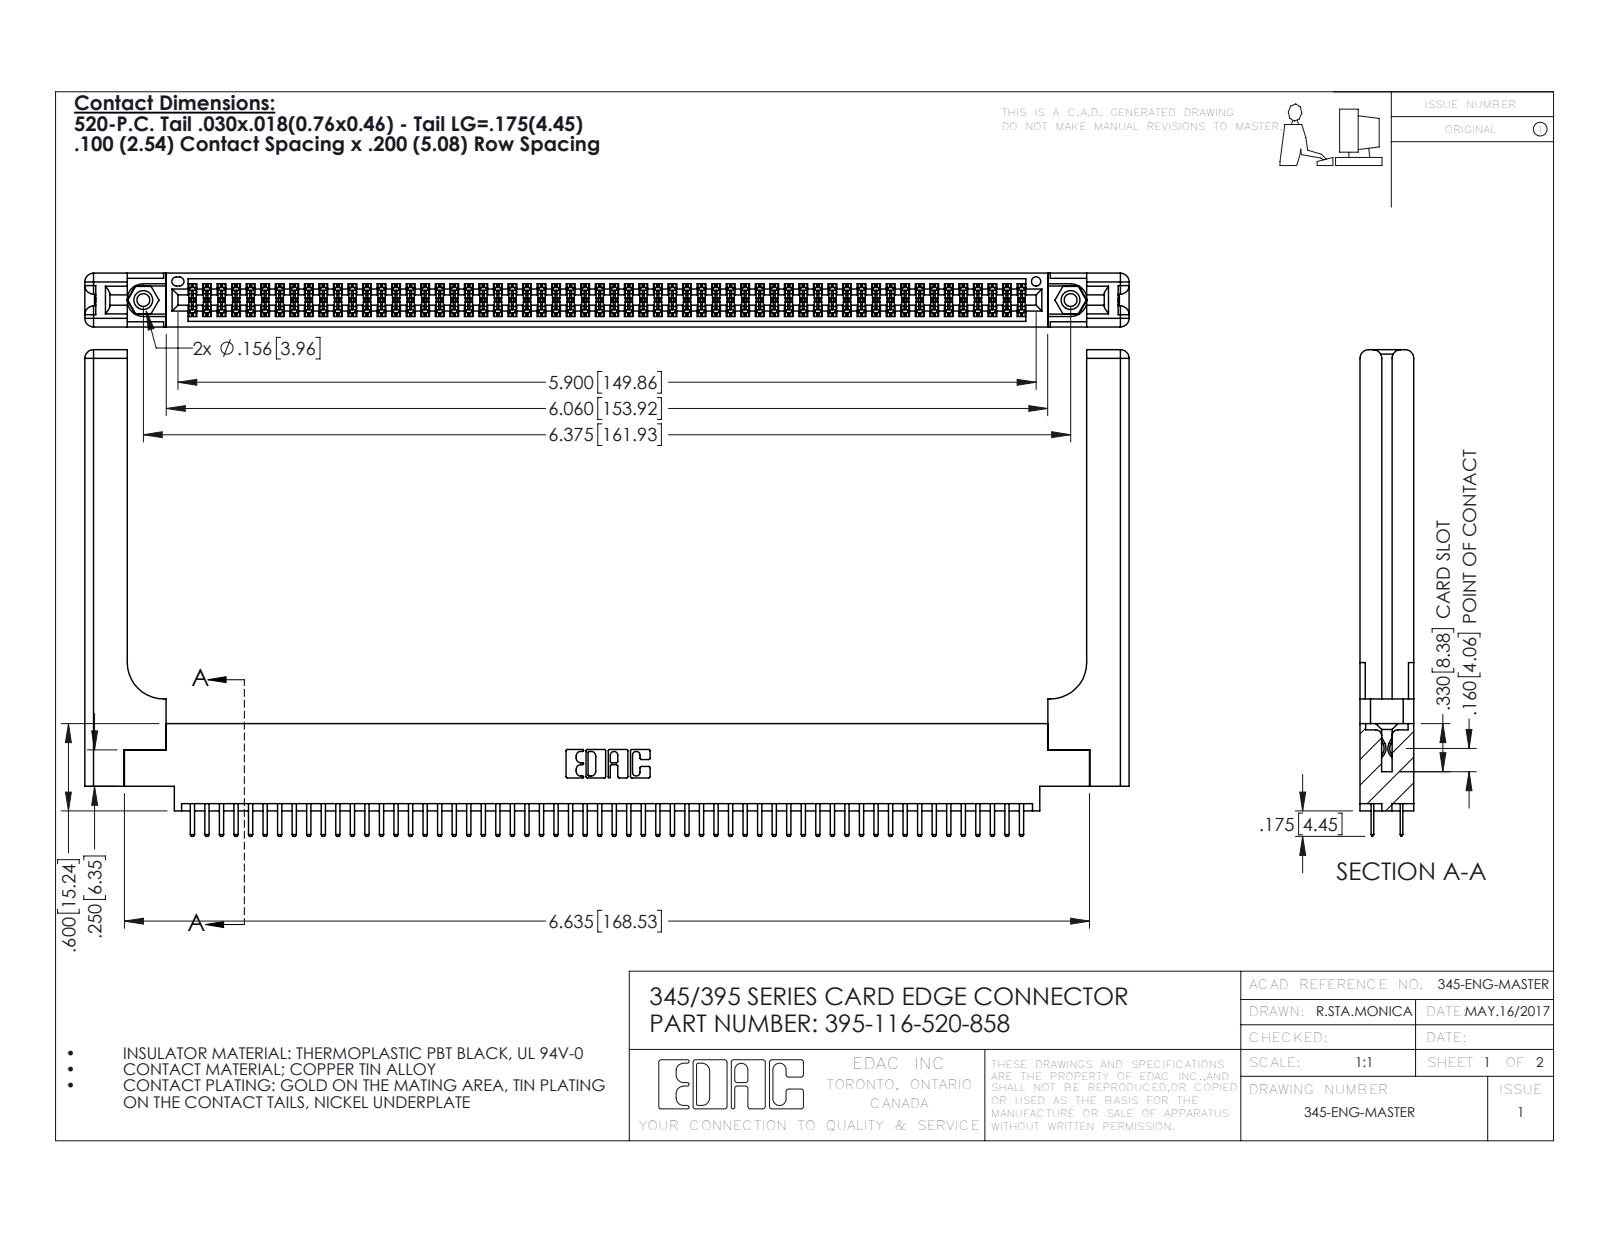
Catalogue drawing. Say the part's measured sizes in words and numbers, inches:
The part is named "345-250-001_345-250-001-102; 395-116-520-858; 345 Part_0.170 Offset - 0.156 Dia-TH; 345-292-001_345-293-120 (+1 more)". Its 3-D file was written by "SolidWorks 2016 (CONFIG_CONTROL_DESIGN)". It is 121 solids with 6650 faces: 4292 planar, 2298 cylindrical and 60 other. Overall it measures 7.179 by 3.345 by 0.37 inches. Its volume is 1.597 cubic inches and its surface area 48.92 square inches. Round holes: 2 of diameter 0.089, 2 of diameter 0.125, 2 of diameter 0.156, 1 of diameter 0.064. Round bosses or shafts: 2 of diameter 0.155. Partial cylindrical surfaces (rounded edges, fillets, slot ends): 174 of radius 0.006, 120 of radius 0.01, 22 of radius 0.01, 16 of radius 0.06, 6 of radius 0.007, 6 of radius 0.031, 3 of radius 0.026, 2 of radius 0.014. The main face-to-face distances are 0.072, 0.37, 0.298, 0.2, 0.098, 0.272, 0.025, 0.225, 0.022, 0.175. The hole center spacings are 0.27, 6.139, 6.375.
